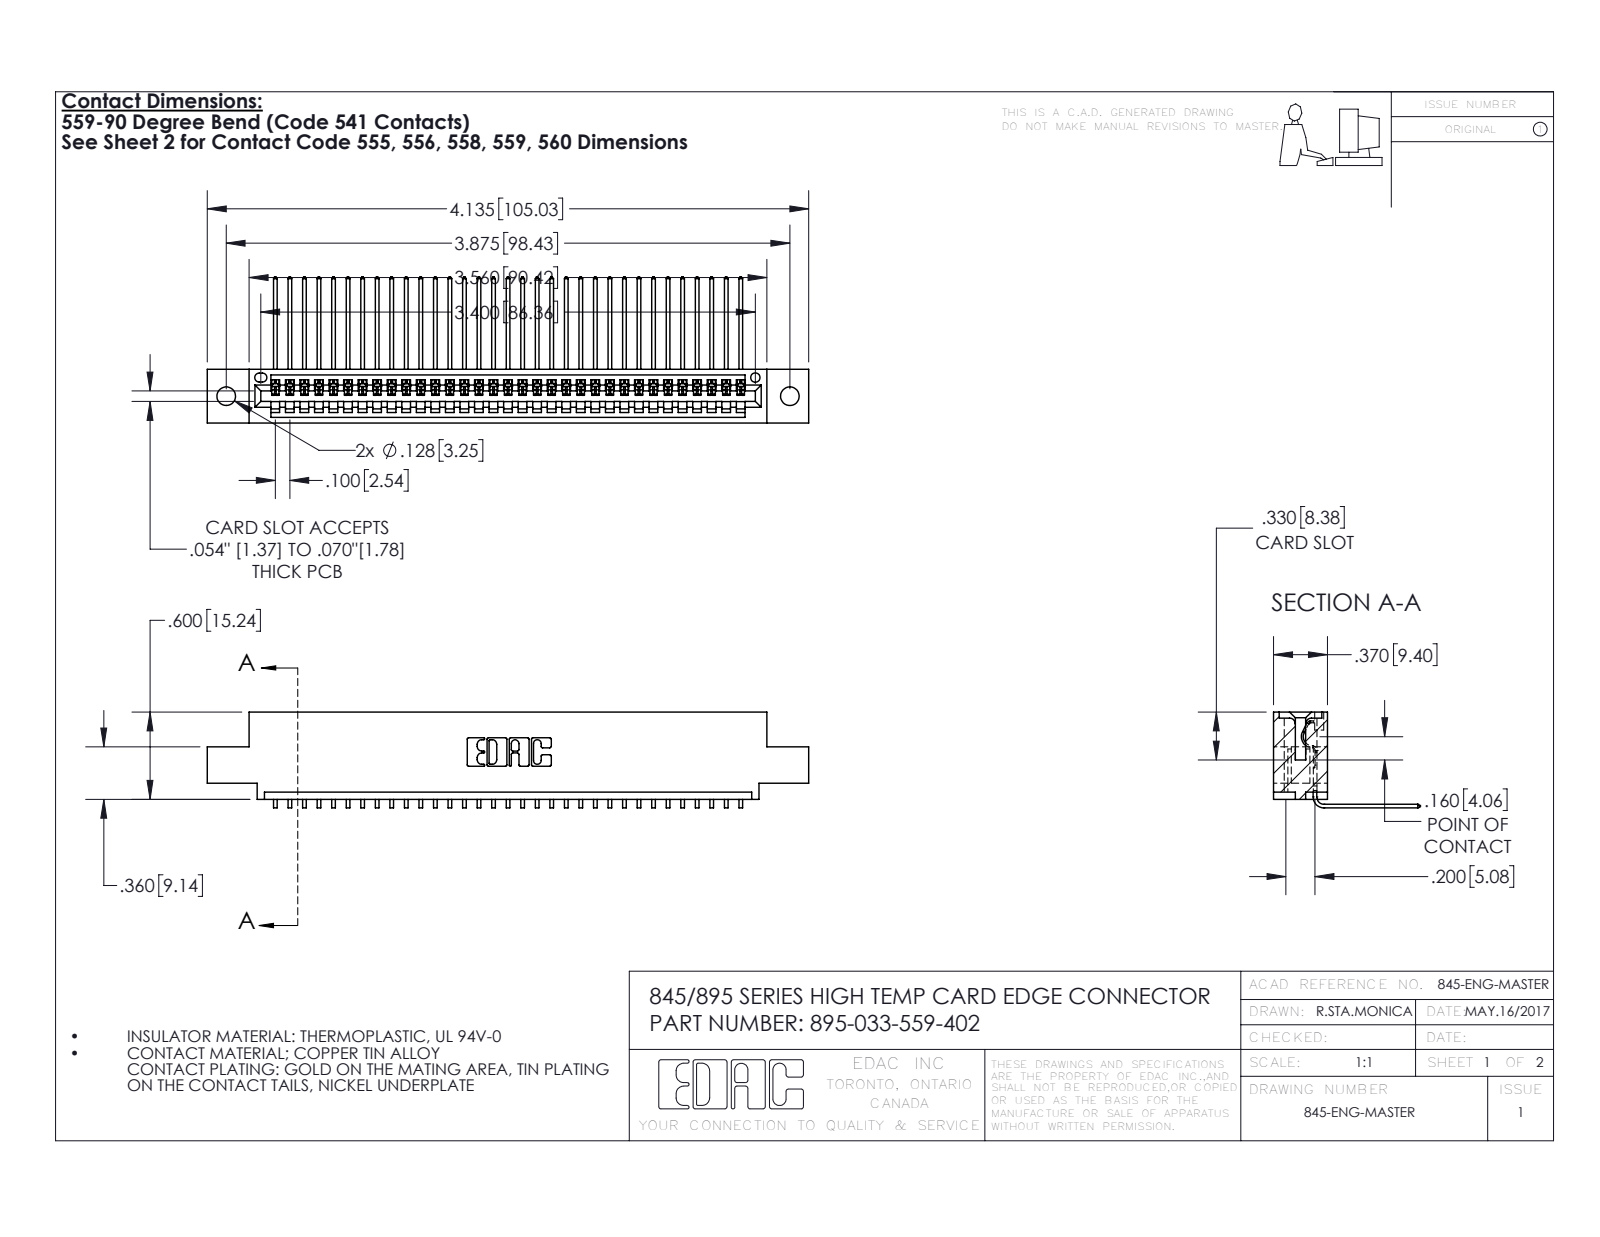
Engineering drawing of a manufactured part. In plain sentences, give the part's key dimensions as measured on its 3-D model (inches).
The part is named "395-033-559-402; 345-292-001_558 559 Tail - 1; 345 Part_0.110 Offset - 0.128 Dia". Its 3-D file was written by "SolidWorks 2016 (CONFIG_CONTROL_DESIGN)". It is 34 solids with 2110 faces: 1470 planar, 640 cylindrical and 0 other. Overall it measures 4.135 by 1.005 by 0.659 inches. Its volume is 0.604 cubic inches and its surface area 20.91 square inches. Round holes: 2 of diameter 0.128, 1 of diameter 0.064. Partial cylindrical surfaces (rounded edges, fillets, slot ends): 66 of radius 0.006, 22 of radius 0.01, 6 of radius 0.007, 6 of radius 0.031, 3 of radius 0.026, 2 of radius 0.031, 2 of radius 0.04, 1 of radius 0.014. The main face-to-face distances are 0.072, 0.298, 0.37, 0.2, 0.098, 0.272, 0.025, 0.225, 0.149, 0.072. The hole center spacings are 0.27, 3.64, 3.875.
